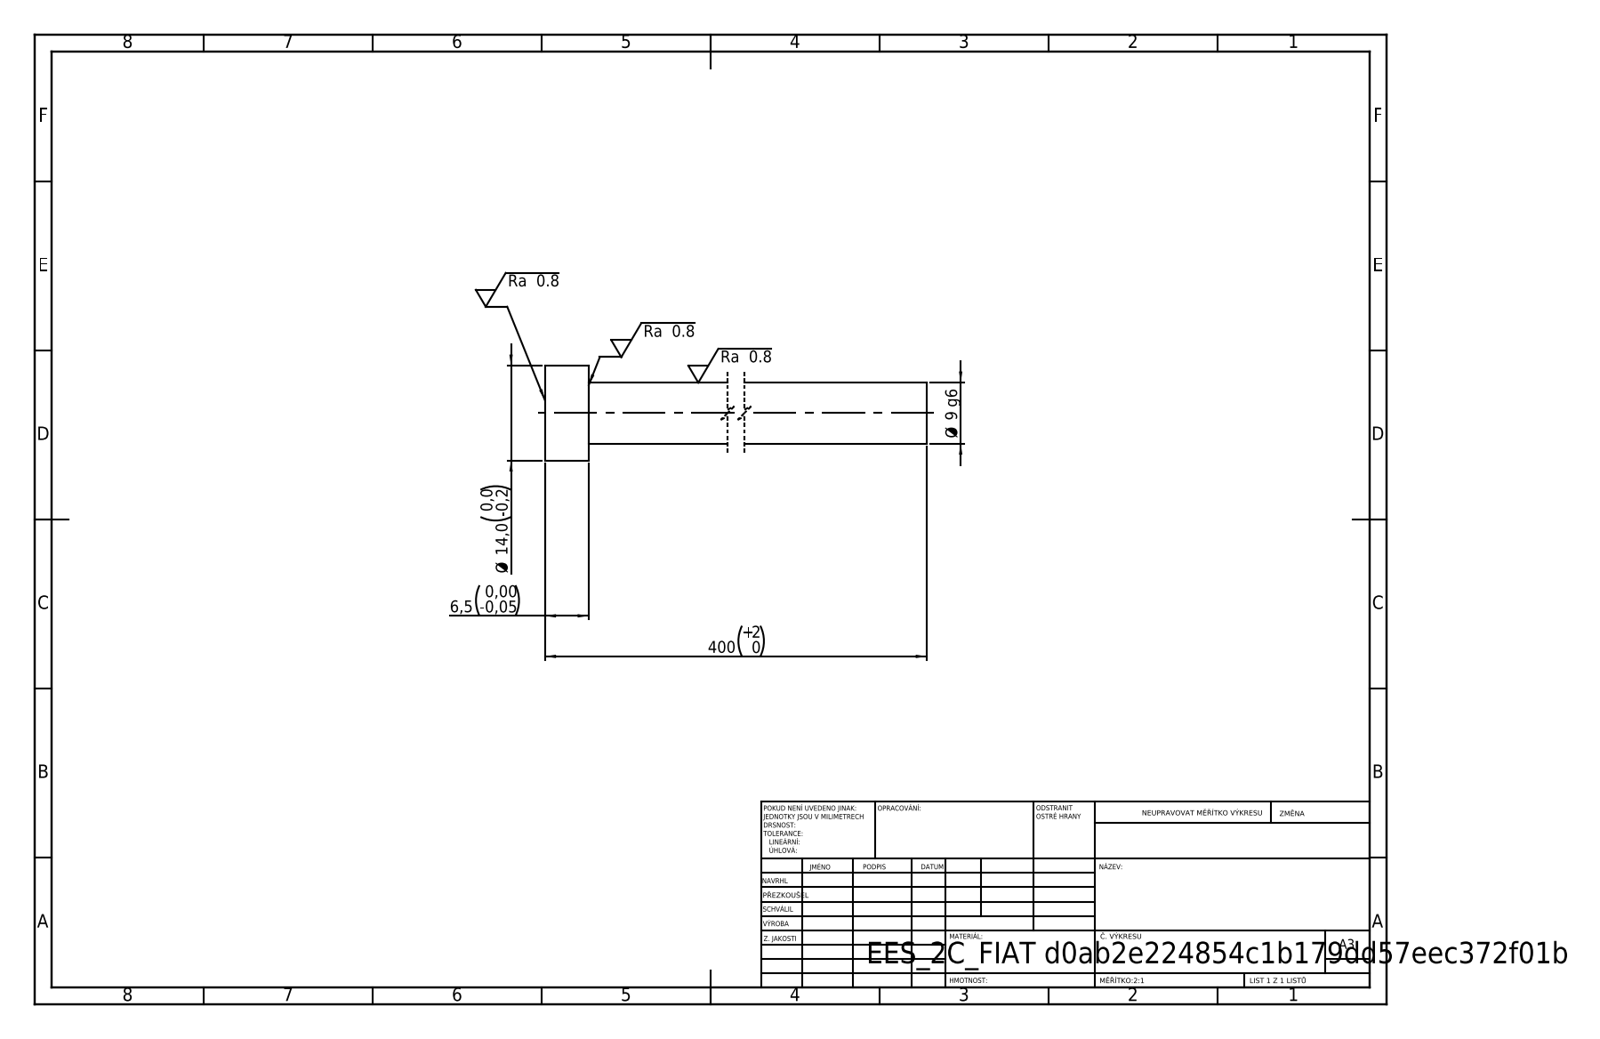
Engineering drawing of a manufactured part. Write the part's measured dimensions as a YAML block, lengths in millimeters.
step_written_by: "SolidWorks 2019 (CONFIG_CONTROL_DESIGN)"
units: millimeters
bodies: {solids: 1, faces: 7, planar: 3, cylindrical: 4, other: 0}
overall_size: [400, 14, 14]
volume: 26034
surface_area: 11720
round_bosses_or_shafts:
  - {diameter: 14, count: 1}
  - {diameter: 9, count: 1}
face_to_face_distances: [6.5, 400, 393.5]
